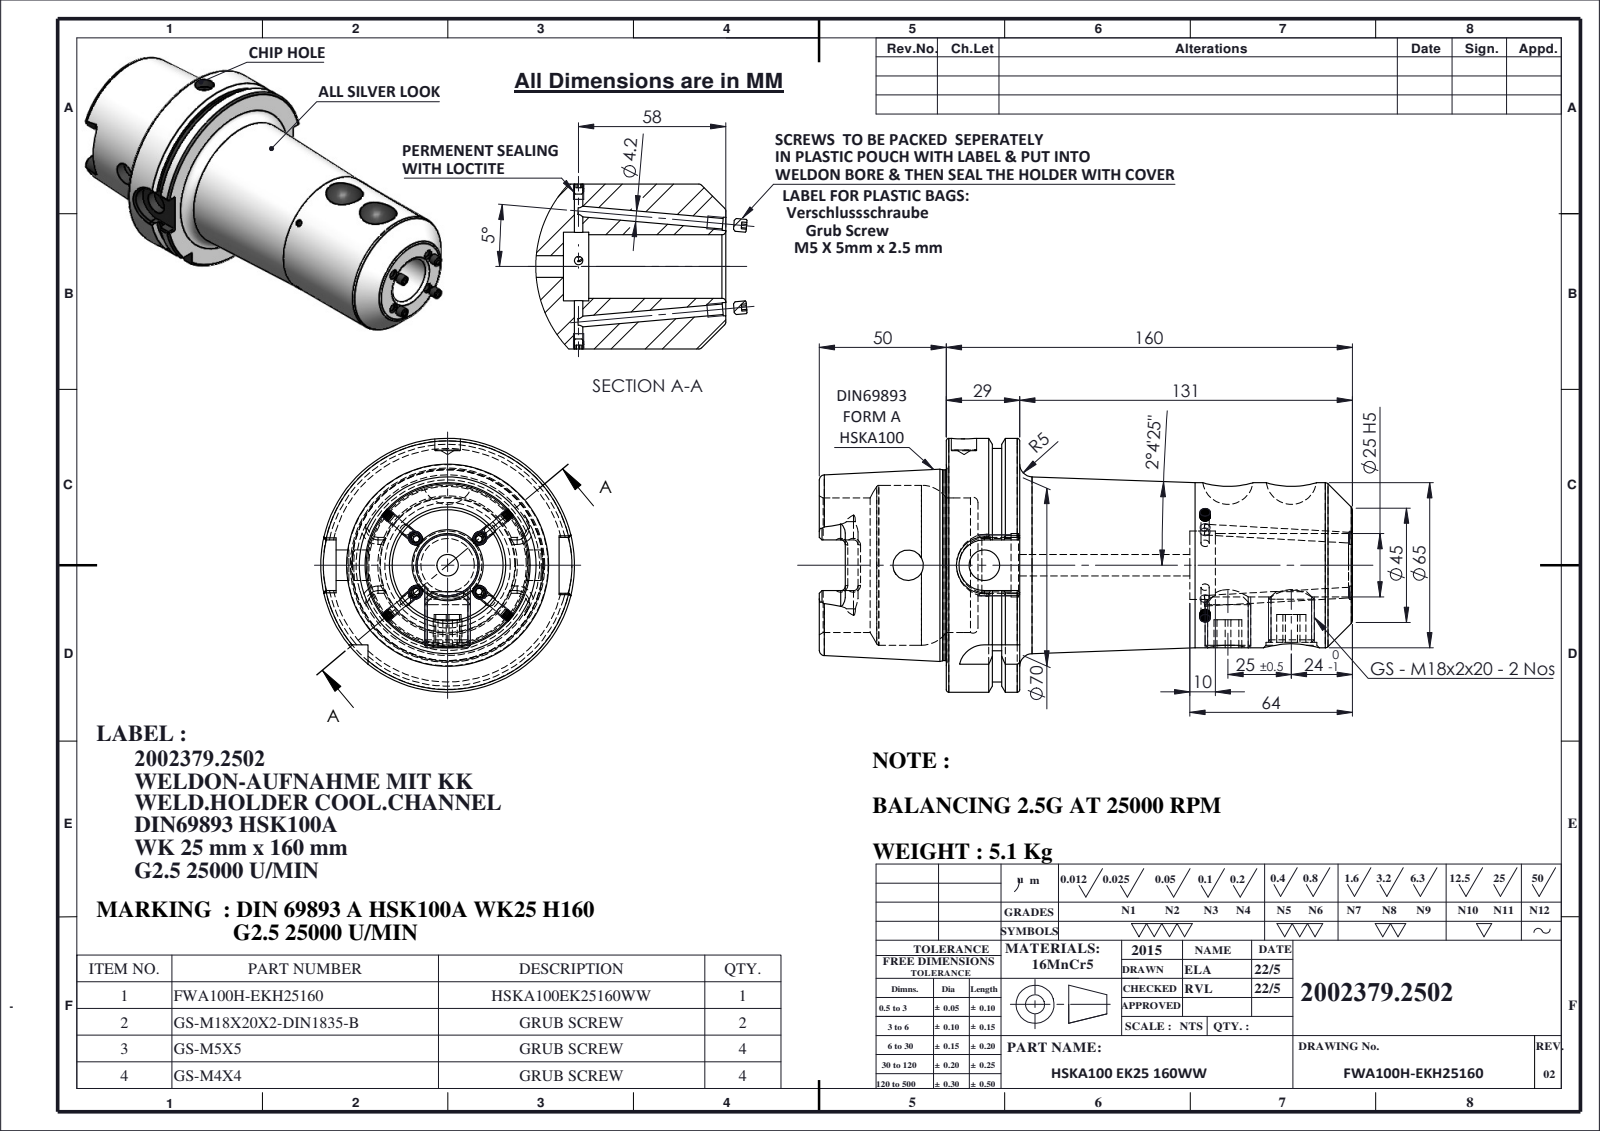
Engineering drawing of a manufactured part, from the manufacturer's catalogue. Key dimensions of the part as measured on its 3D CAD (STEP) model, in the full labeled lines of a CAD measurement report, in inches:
Part name (STEP PRODUCT): HSKA100EK25160WW-M&G-R04; GS-M18X20X2-DIN1835-B; GS-M5X5_DIN 913 - M5 x 5-N; GS-M4X4_DIN 913 - M4 x 4-N (+2 more)
STEP written by: SolidWorks 2018 (CONFIG_CONTROL_DESIGN)
Units: inches
Bodies: 11 solids, 508 faces (154 planar, 138 cylindrical, 216 other)
Overall size (bounding box): 8.597 × 3.937 × 3.937
Volume: 40 in³ · Surface area: 142.2 in²
Round holes (diameter × count): ⌀0.13 ×4, ⌀0.165 ×4, ⌀0.205 ×4, ⌀0.472 ×2, ⌀0.63 ×2, ⌀0.335 ×1, ⌀0.394 ×1, ⌀0.787 ×1, ⌀0.827 ×1, ⌀0.984 ×1, ⌀1.063 ×1, ⌀2.087 ×1
Round bosses / shafts (diameter × count): ⌀0.197 ×4, ⌀0.157 ×4, ⌀0.709 ×2, ⌀3.937 ×1, ⌀3.622 ×1, ⌀2.959 ×1, ⌀2.559 ×1
Partial cylindrical surfaces — rounded edges, fillets, slot ends (radius × count): R0.071 ×6, R0.192 ×4, R0.394 ×2, R0.433 ×1
Main face-to-face distances: 1.14, 0.492, 0.648, 1.969, 2.461, 3.108, 8.268, 6.299, 5.807, 5.159
Hole centre spacings: 0.984, 1.181, 4.094, 5.079
